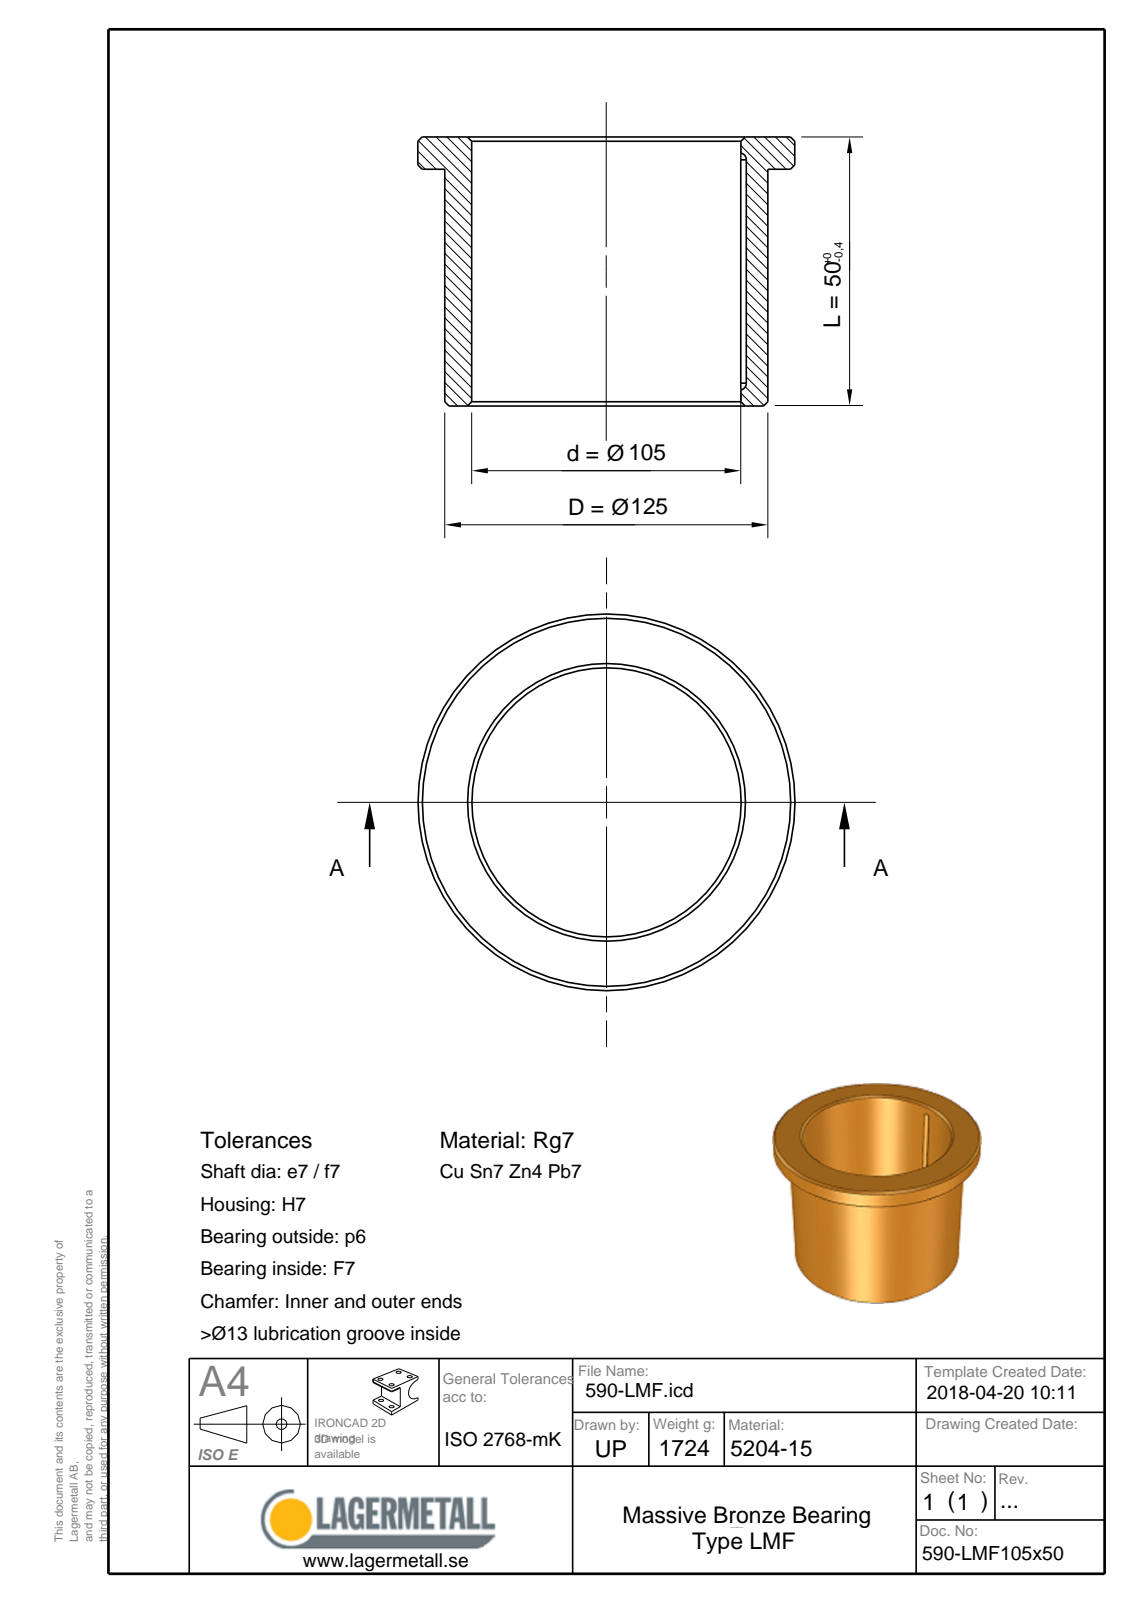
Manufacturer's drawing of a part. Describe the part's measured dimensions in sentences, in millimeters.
The part is named "590-LMF105x50". Its 3-D file was written by "Spatial InterOp 3D (CONFIG_CONTROL_DESIGN)". It is 1 solid with 16 faces: 4 planar, 5 cylindrical and 7 other. Overall it measures 135 by 135 by 50 millimeters. Its volume is 195 865 cubic millimeters and its surface area 46 643 square millimeters. Round holes: 1 of diameter 105. Round bosses or shafts: 1 of diameter 135, 1 of diameter 125. Partial cylindrical surfaces (rounded edges, fillets, slot ends): 2 of radius 1.75. The main face-to-face distances are 50, 42, 8.
